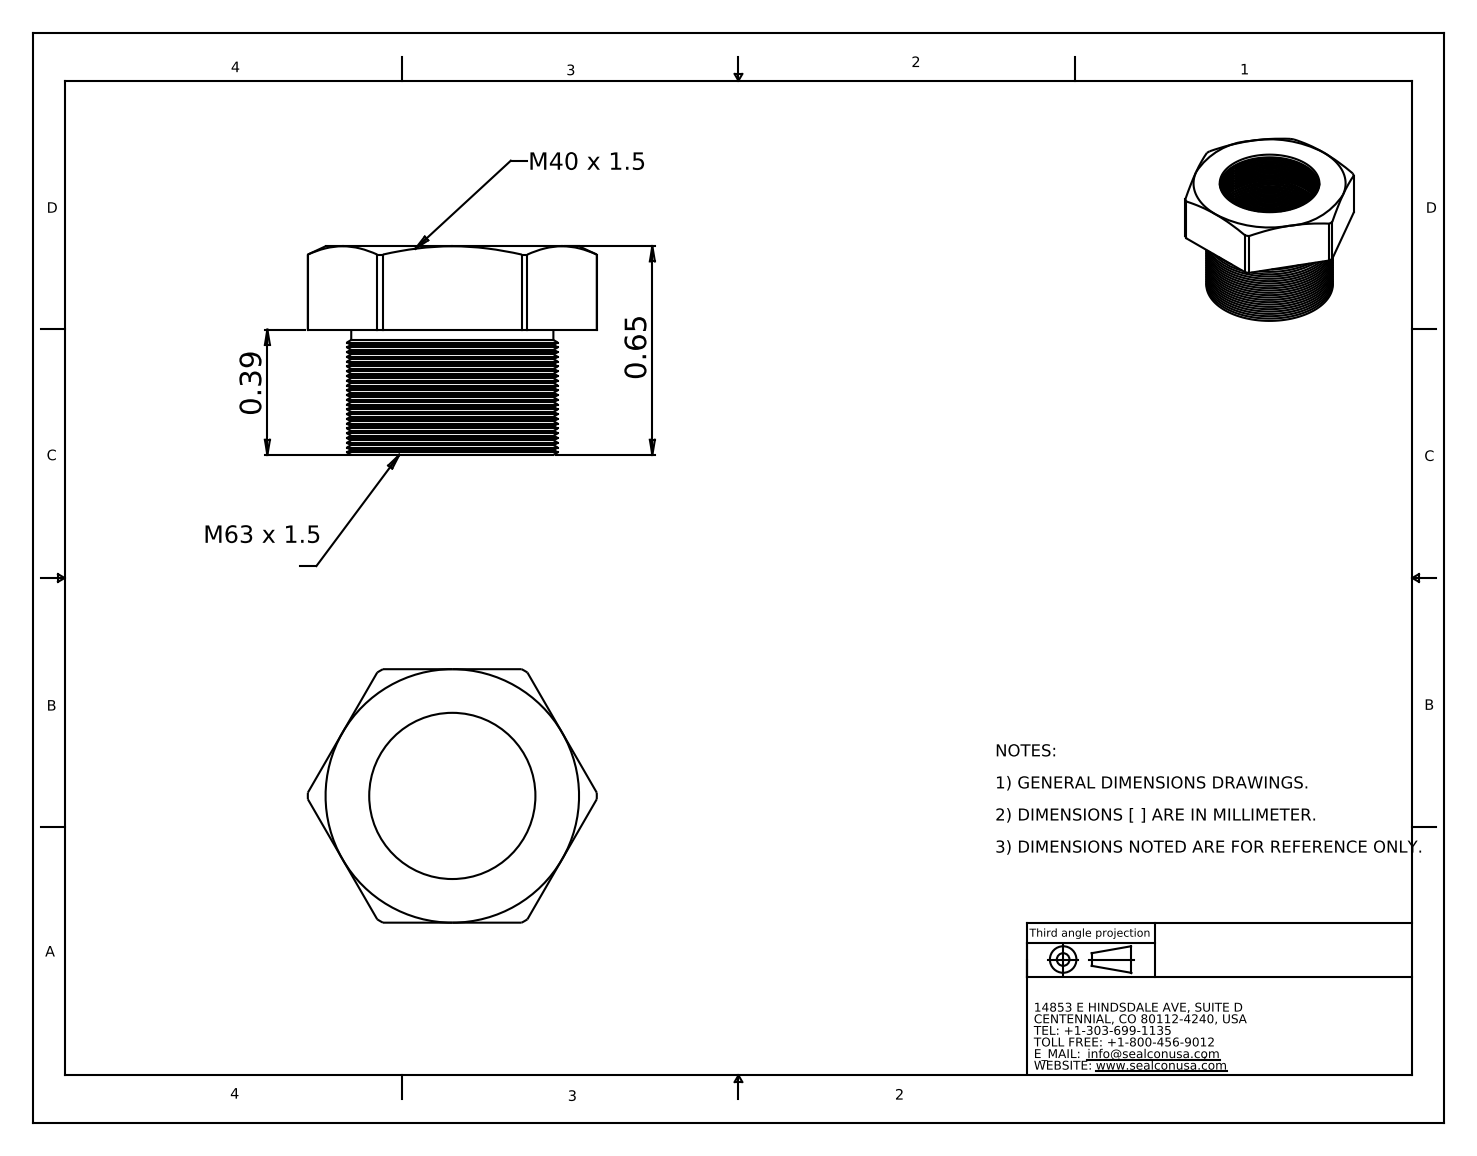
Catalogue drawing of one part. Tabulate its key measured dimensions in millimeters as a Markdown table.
| quantity | value |
| --- | --- |
| part name | RM-6340-SS |
| STEP written by | SolidWorks 2008 (CONFIG_CONTROL_DESIGN) |
| units | millimeters |
| bodies | 1 solid, 363 faces (9 planar, 91 cylindrical, 263 other) |
| overall size | 22.9 × 20.1 × 16.5 |
| volume | 2 080 mm³ |
| surface area | 3 225 mm² |
| round holes (diameter × count) | 13.2 × 1, 16 × 1 |
| partial cylindrical surfaces (radius × count) | 11.4 × 1 |
| main face-to-face distances | 20.1, 6.6, 9.9, 16.5 |
